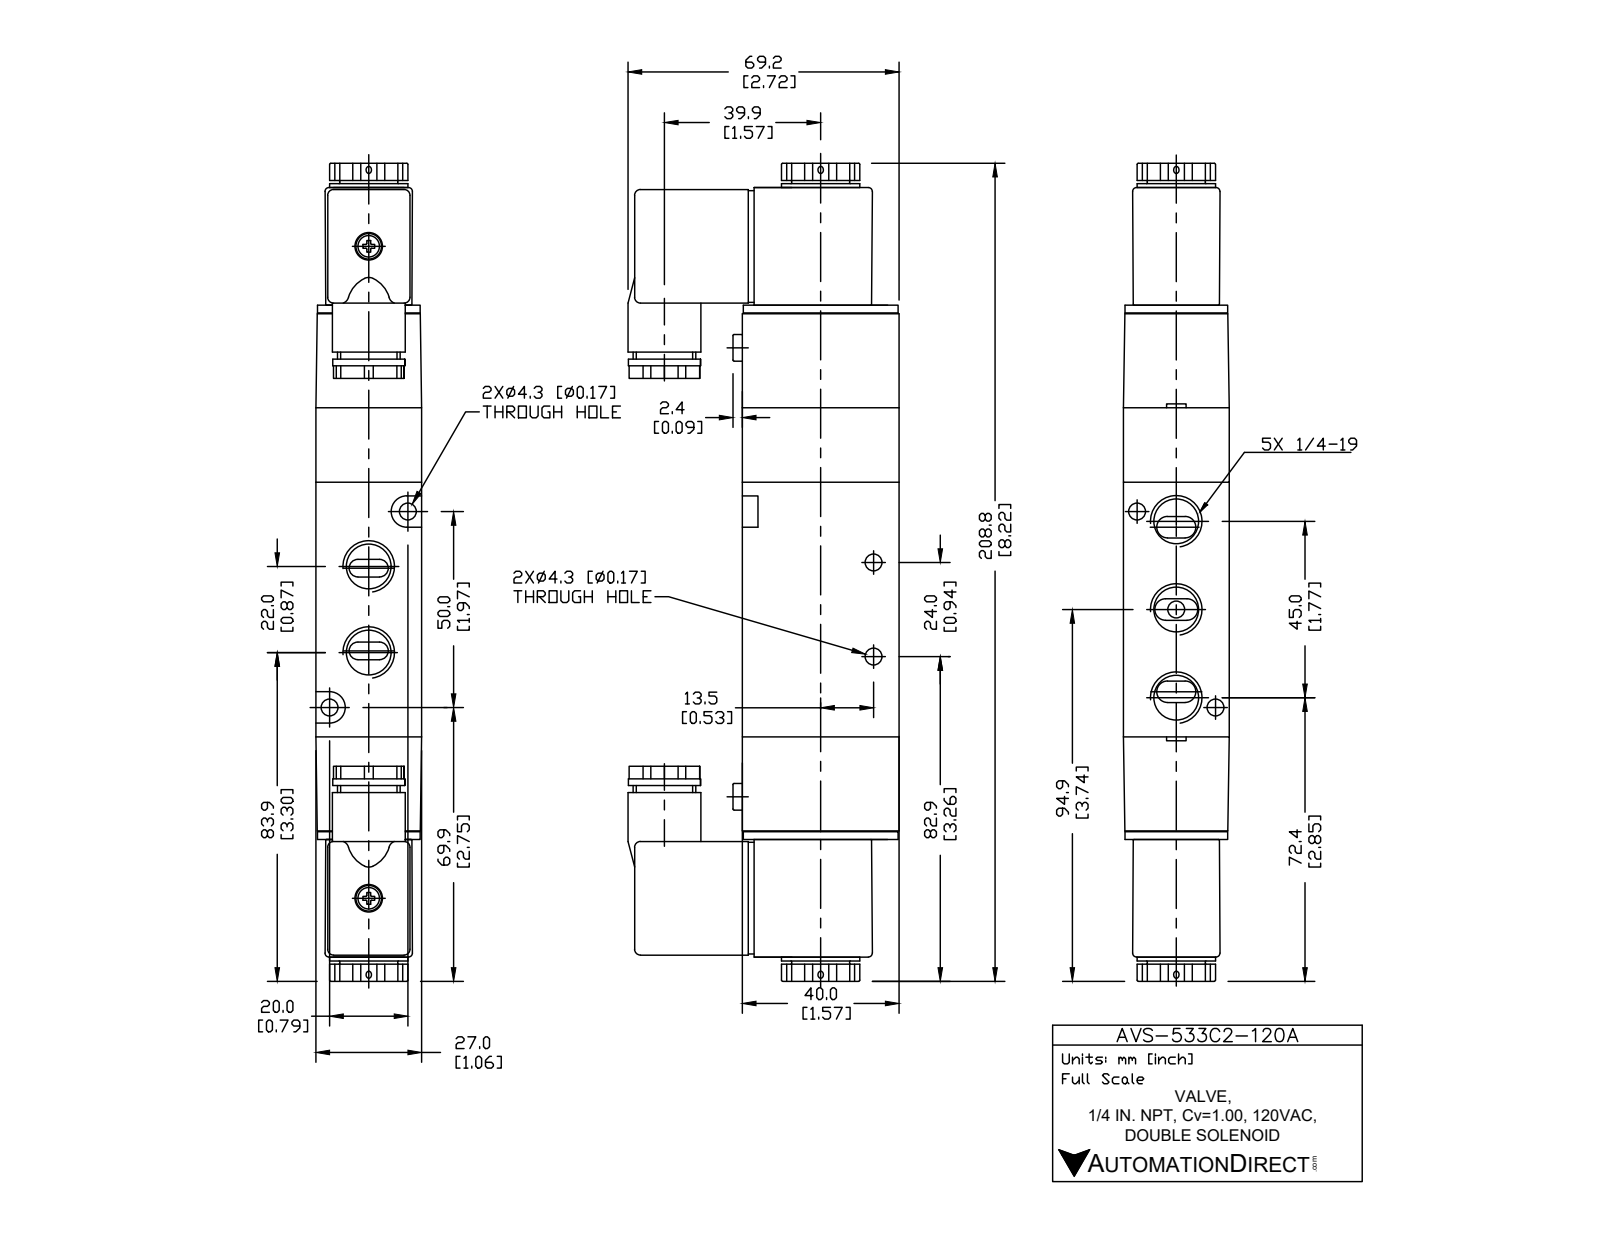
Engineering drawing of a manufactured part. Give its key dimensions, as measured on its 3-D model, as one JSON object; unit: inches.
{"part_name": "AVS-533C2-120A", "step_written_by": "SolidWorks 2015 (CONFIG_CONTROL_DESIGN)", "units": "inches", "bodies": {"solids": 5, "faces": 278, "planar": 133, "cylindrical": 111, "other": 34}, "overall_size": [8.22, 2.724, 1.063], "volume_in3": 13.7, "surface_area_in2": 70.72, "round_holes": [[0.438, 5], [0.169, 4], [0.366, 1]], "round_bosses_or_shafts": [[0.264, 2], [0.787, 1], [0.732, 1], [0.724, 1], [0.63, 1], [0.583, 1]], "partial_cylinders_radius": [[0.059, 18], [0.118, 12], [0.039, 10], [0.02, 8]], "face_to_face_distances": [1.063, 0.118, 0.945, 1.575, 3.307, 0.914, 0.827, 1.161, 0.02, 6.551], "hole_center_spacings": [0.406, 0.433, 0.453, 0.677, 0.886, 1.06, 1.319, 1.471]}
